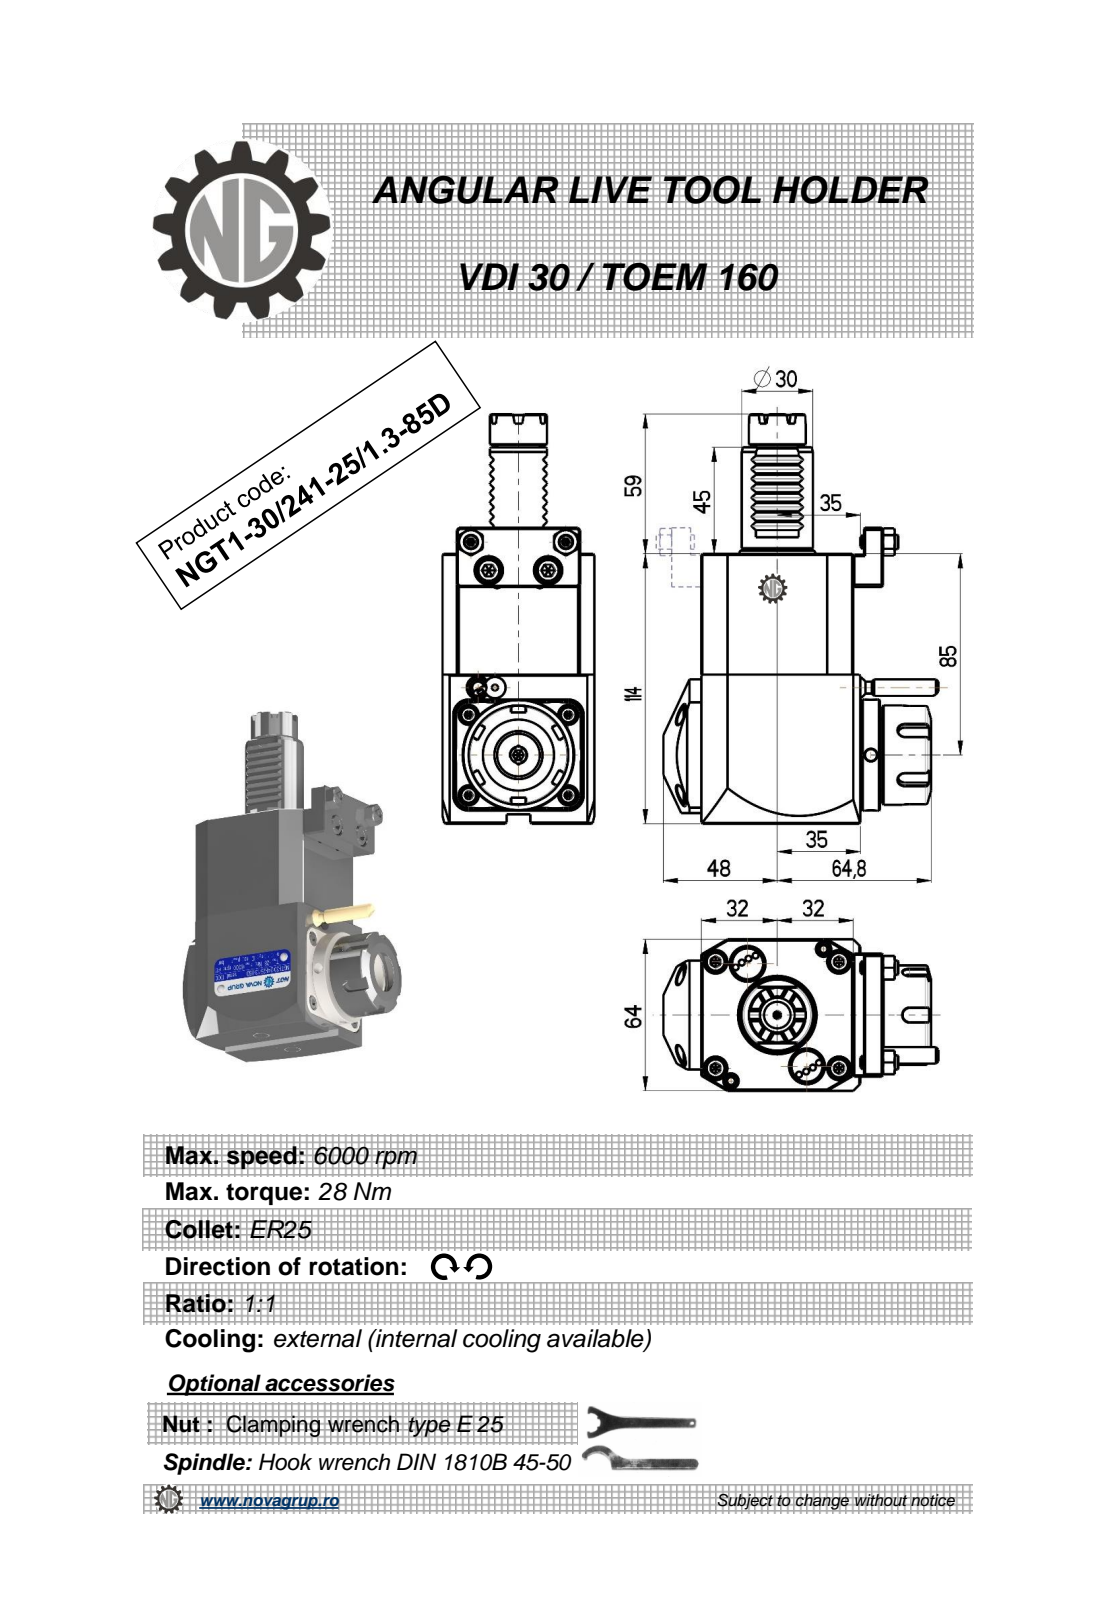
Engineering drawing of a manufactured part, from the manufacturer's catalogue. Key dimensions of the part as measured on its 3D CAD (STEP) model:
Part name (STEP PRODUCT): NGT1_30_241_25_1_3_85D
STEP written by: PRO/ENGINEER BY PARAMETRIC TECHNOLOGY CORPORATION, 2010280 (CONFIG_CONTROL_DESIGN)
Units: millimetres
Bodies: 1 solid, 490 faces (230 planar, 88 cylindrical, 172 other)
Overall size (bounding box): 173 × 115.83 × 64
Volume: 578 186 mm³ · Surface area: 55 823 mm²
Round holes (diameter × count): ⌀5 ×2, ⌀2.5 ×1, ⌀3 ×1, ⌀20.3 ×1
Round bosses / shafts (diameter × count): ⌀6 ×2, ⌀47 ×1, ⌀42 ×1, ⌀35 ×1, ⌀30 ×1, ⌀24 ×1, ⌀17.7 ×1, ⌀15.2 ×1
Partial cylindrical surfaces — rounded edges, fillets, slot ends (radius × count): R0.3 ×16, R0.31 ×10, R3 ×5, R3.5 ×2, R160 ×2, R32 ×1
Main face-to-face distances: 64, 114, 3, 0.5, 9.3, 8, 3.2, 67.2, 76.42, 1.3
Hole centre spacings: 33.19
